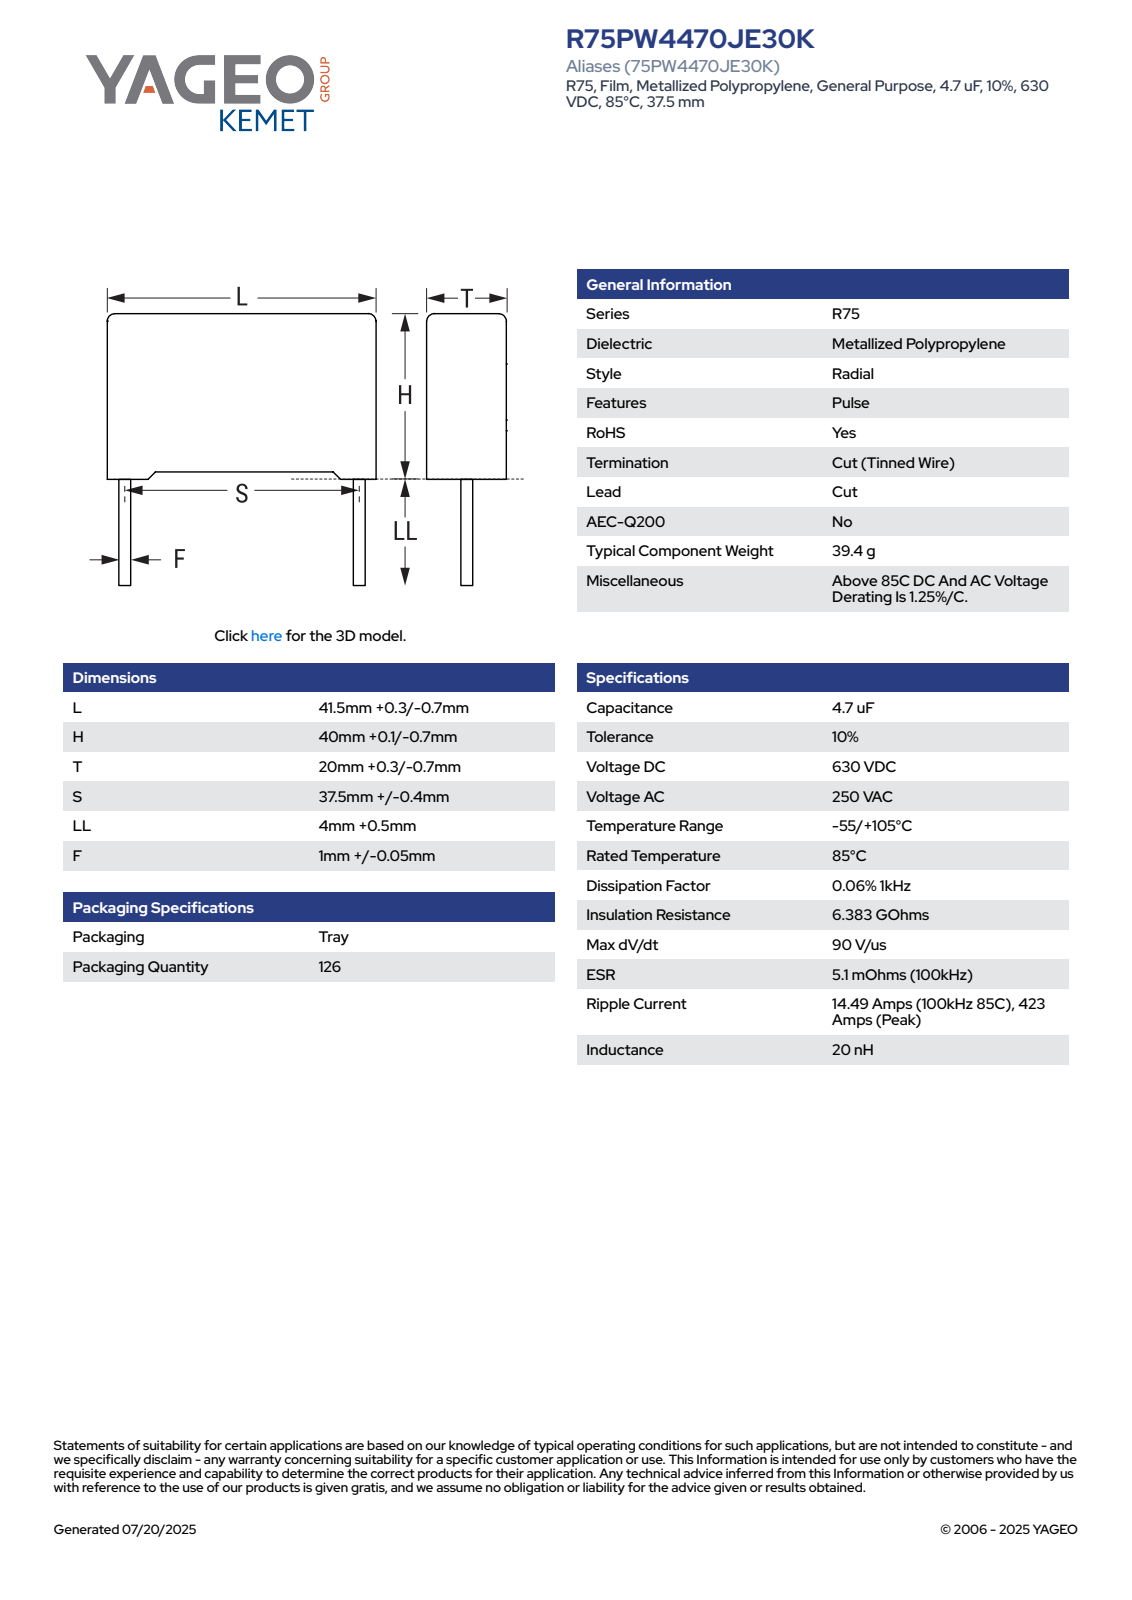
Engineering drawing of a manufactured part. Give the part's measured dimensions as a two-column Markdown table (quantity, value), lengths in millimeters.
| quantity | value |
| --- | --- |
| part name | CFR_RB2_41.5X40X20_L41.8H40.1T20.3S37.5LL4.5F1.05 |
| STEP written by | SolidWorks 2021 (AUTOMOTIVE_DESIGN) |
| units | millimeters |
| bodies | 4 solids, 85 faces (77 planar, 8 cylindrical, 0 other) |
| overall size | 44.6 × 41.8 × 20.3 |
| volume | 33 026 mm³ |
| surface area | 6 772 mm² |
| round bosses / shafts (diameter × count) | 1.05 × 2 |
| partial cylindrical surfaces (radius × count) | 0.5 × 4 |
| main face-to-face distances | 20.3, 41.8, 38.72, 0.63, 39.35, 0.75, 1.38, 40.1, 1.39, 20.31 |
